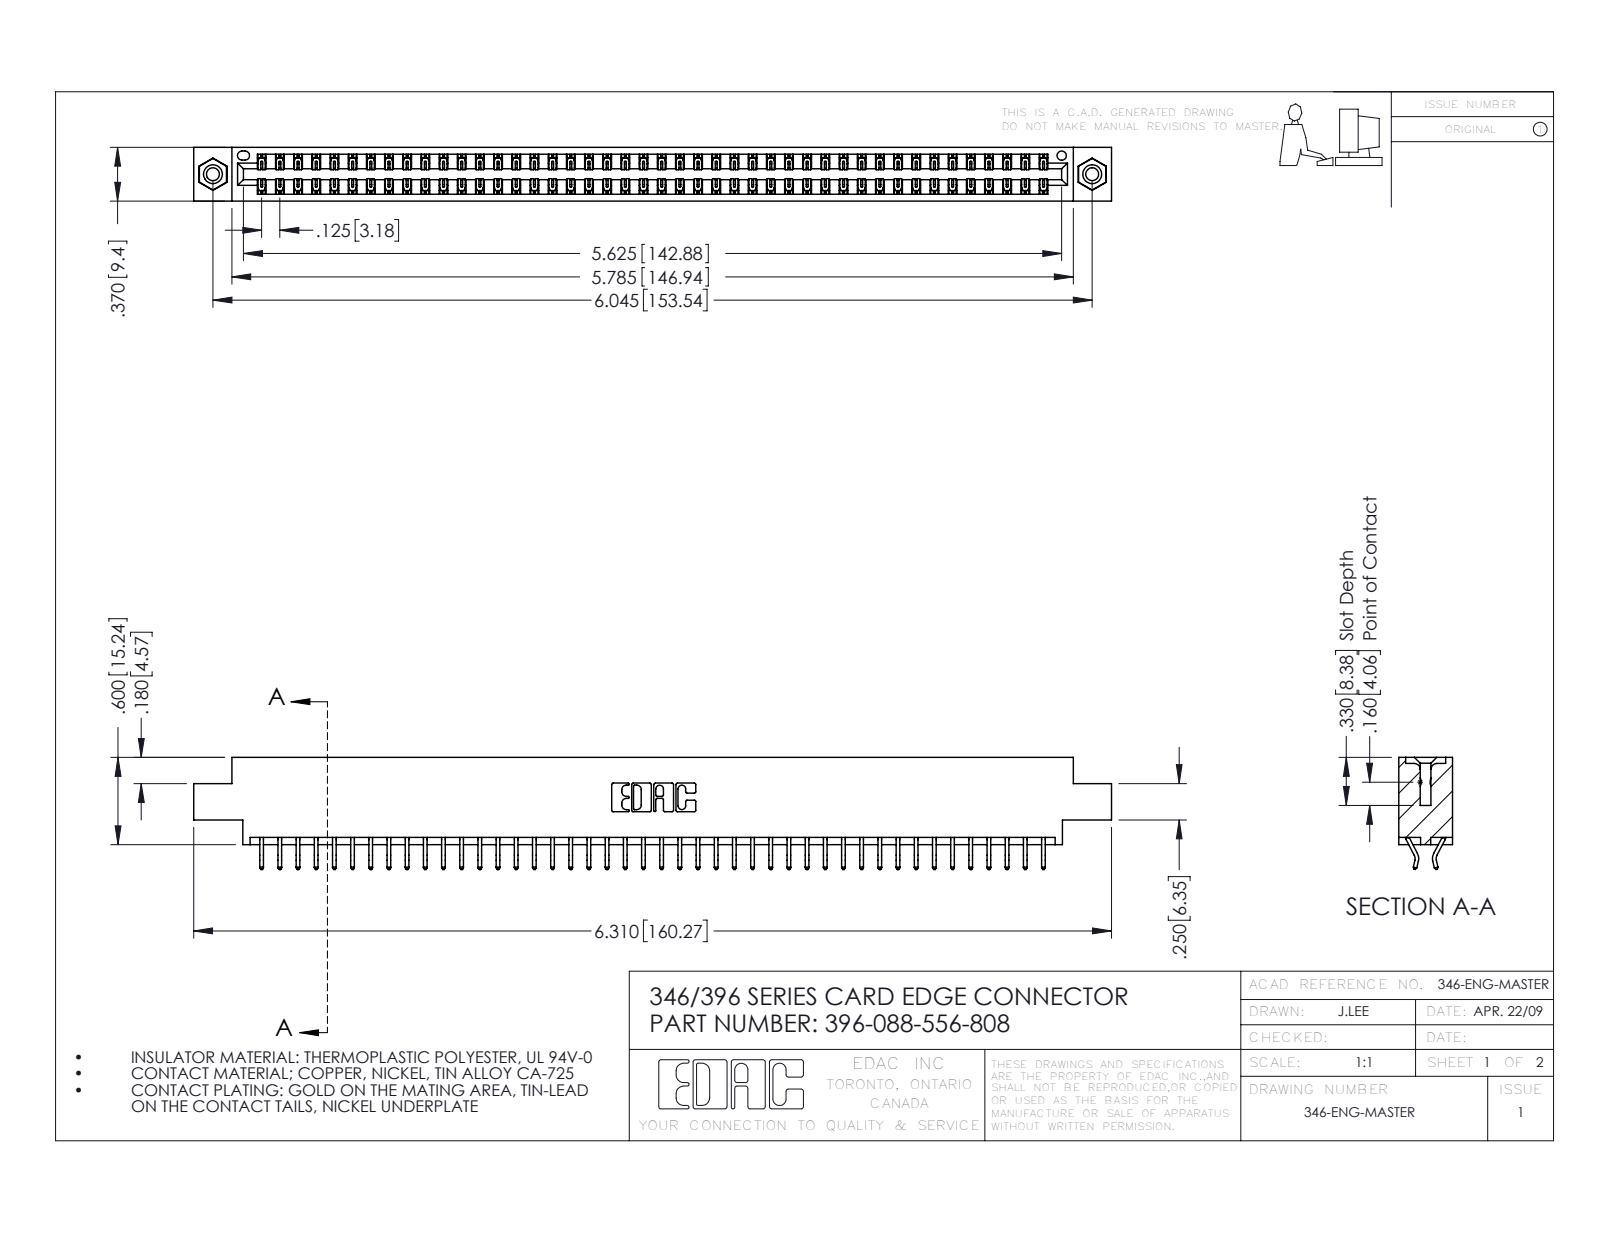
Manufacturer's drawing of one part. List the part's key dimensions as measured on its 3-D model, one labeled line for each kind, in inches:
Part name (STEP PRODUCT): 346 Part_0.170 Offset - 0.156 Dia-TI; 396-088-556-808; 345-250-001_345-250-003-102; 345-292-001_556 Tail
STEP written by: SolidWorks 2016 (CONFIG_CONTROL_DESIGN)
Units: inches
Bodies: 91 solids, 5290 faces (3544 planar, 1730 cylindrical, 16 other)
Overall size (bounding box): 6.31 × 0.77 × 0.37
Volume: 0.945 in³ · Surface area: 33.21 in²
Round holes (diameter × count): ⌀0.089 ×2, ⌀0.125 ×2, ⌀0.156 ×2, ⌀0.064 ×1
Round bosses / shafts (diameter × count): ⌀0.155 ×2
Partial cylindrical surfaces — rounded edges, fillets, slot ends (radius × count): R0.006 ×132, R0.01 ×22, R0.007 ×6, R0.031 ×6, R0.026 ×3, R0.01 ×2, R0.014 ×2, R0.022 ×2
Main face-to-face distances: 0.048, 0.322, 0.37, 0.25, 0.025, 0.072, 0.298, 0.275, 0.222, 0.148
Hole centre spacings: 0.246, 5.836, 6.045
